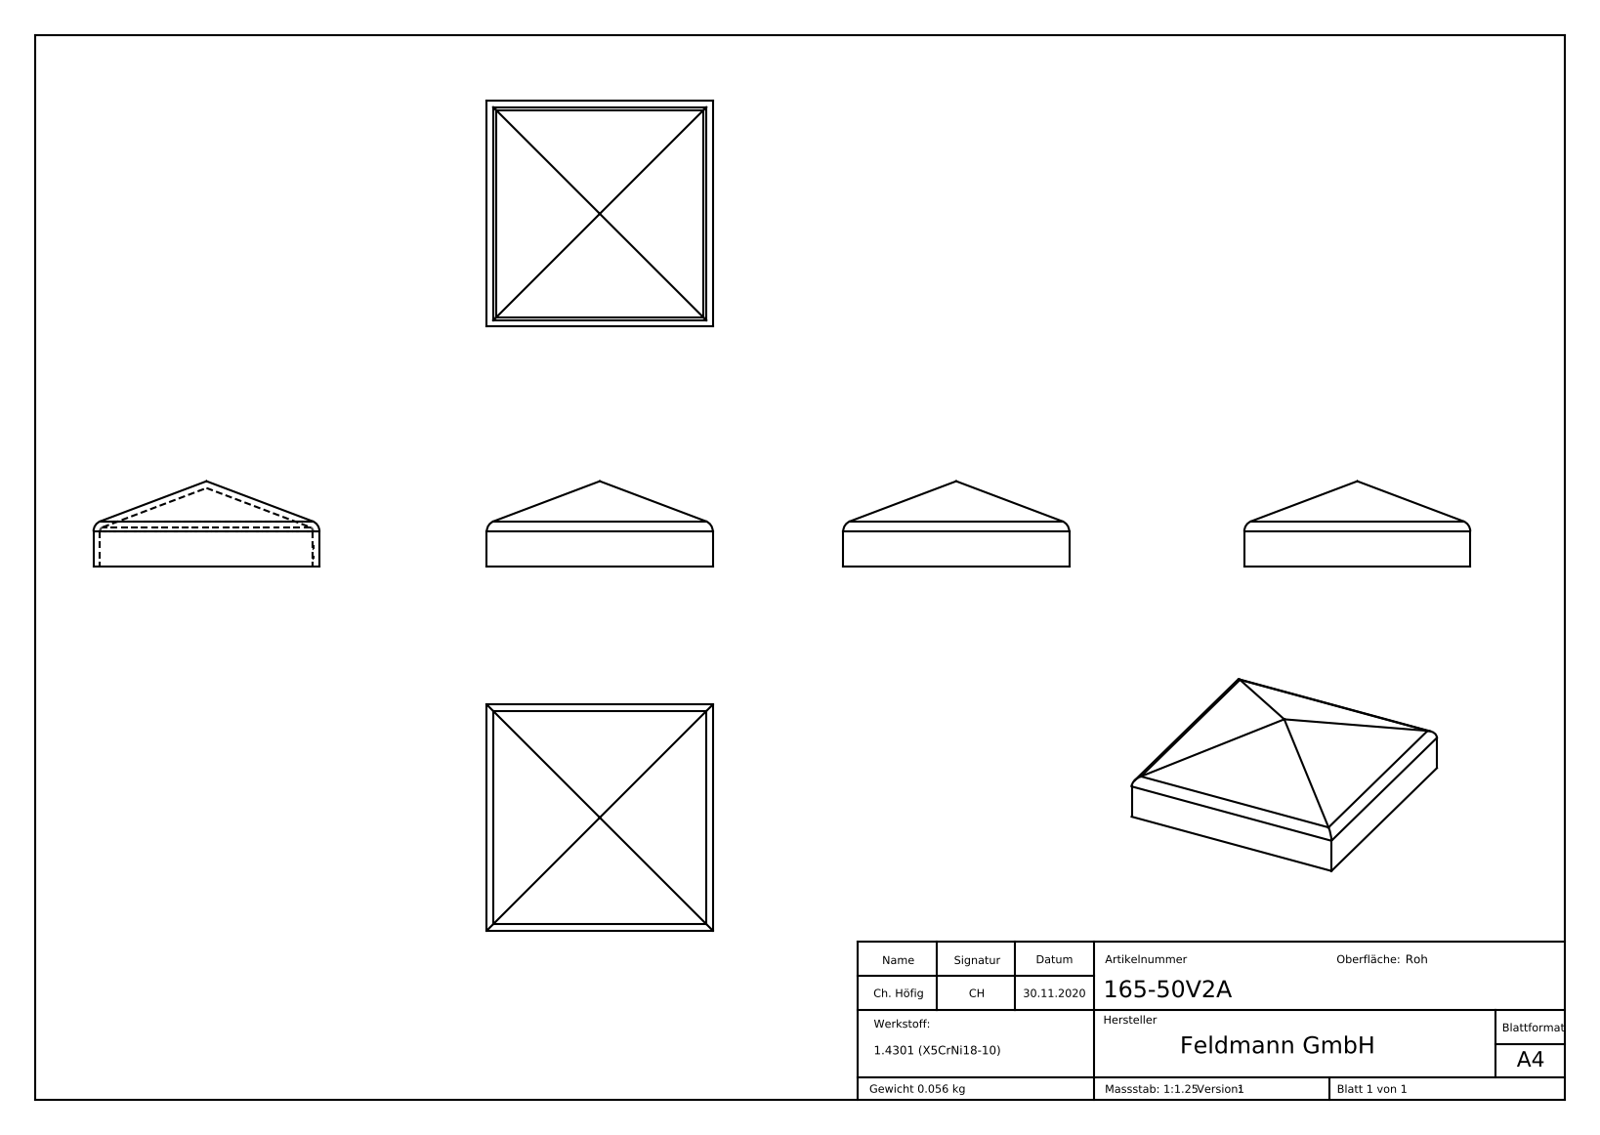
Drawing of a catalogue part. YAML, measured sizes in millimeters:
part_name: "165-50V2A"
step_written_by: "SolidWorks 2018 (CONFIG_CONTROL_DESIGN)"
units: millimeters
bodies: {solids: 1, faces: 243, planar: 143, cylindrical: 12, other: 88}
overall_size: [53, 53, 20]
volume: 7089
surface_area: 9773
partial_cylinders:
  - {radius: 1, count: 4}
  - {radius: 2.5, count: 4}
  - {radius: 0.1, count: 2}
face_to_face_distances: [1.5, 51.5, 1.51, 53, 50, 1.4, 50.1, 51.6, 2.61, 1.78]
